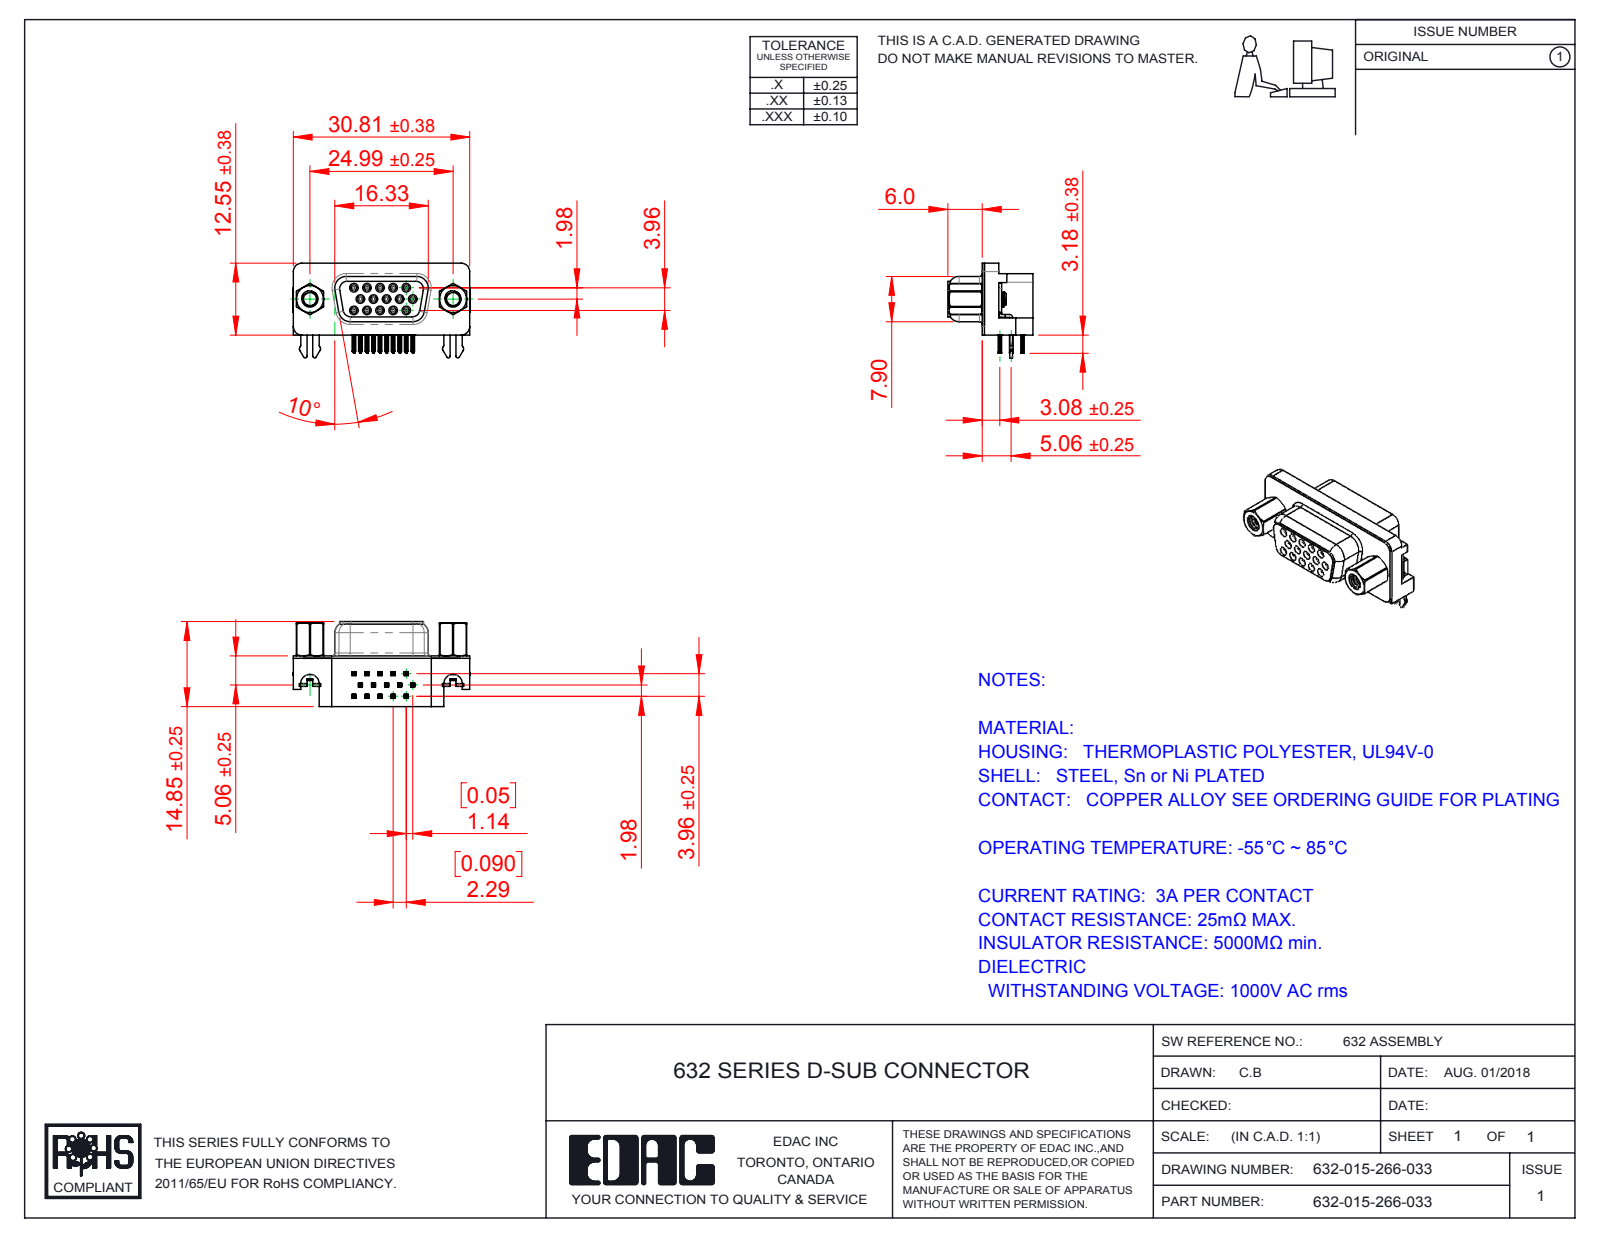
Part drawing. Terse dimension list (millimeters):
name: 632 2 Prong Board Lock; 632 Housing_15 Socket; 632 Contact Top; 632-015-266-003 (+4 more)
written by: SolidWorks 2016 (CONFIG_CONTROL_DESIGN)
unit: mm
bodies: 21 solids, 2376 faces (996 planar, 646 cylindrical, 734 other)
size: 30.89 × 16.55 × 14.85
volume: 3 051 mm³; area: 5 180 mm²
holes: 15× ⌀0.8, 15× ⌀0.9, 2× ⌀2.29, 2× ⌀4, 2× ⌀4.8, 2× ⌀5
bosses: 15× ⌀1.2, 2× ⌀4.9, 2× ⌀2.79
rounds: 120× R0.1, 60× R0.15, 30× R0.35, 15× R0.34, 11× R1, 10× R0.28, 10× R0.5, 8× R1.35
face distances: 0.4, 1.98, 8.45, 8.85, 2.9, 2.5, 5.95, 6.7, 7.05, 3.17
hole spacings: 2.28, 2.29, 3.96, 4.57, 6.05, 3.97, 4.58, 6.86
